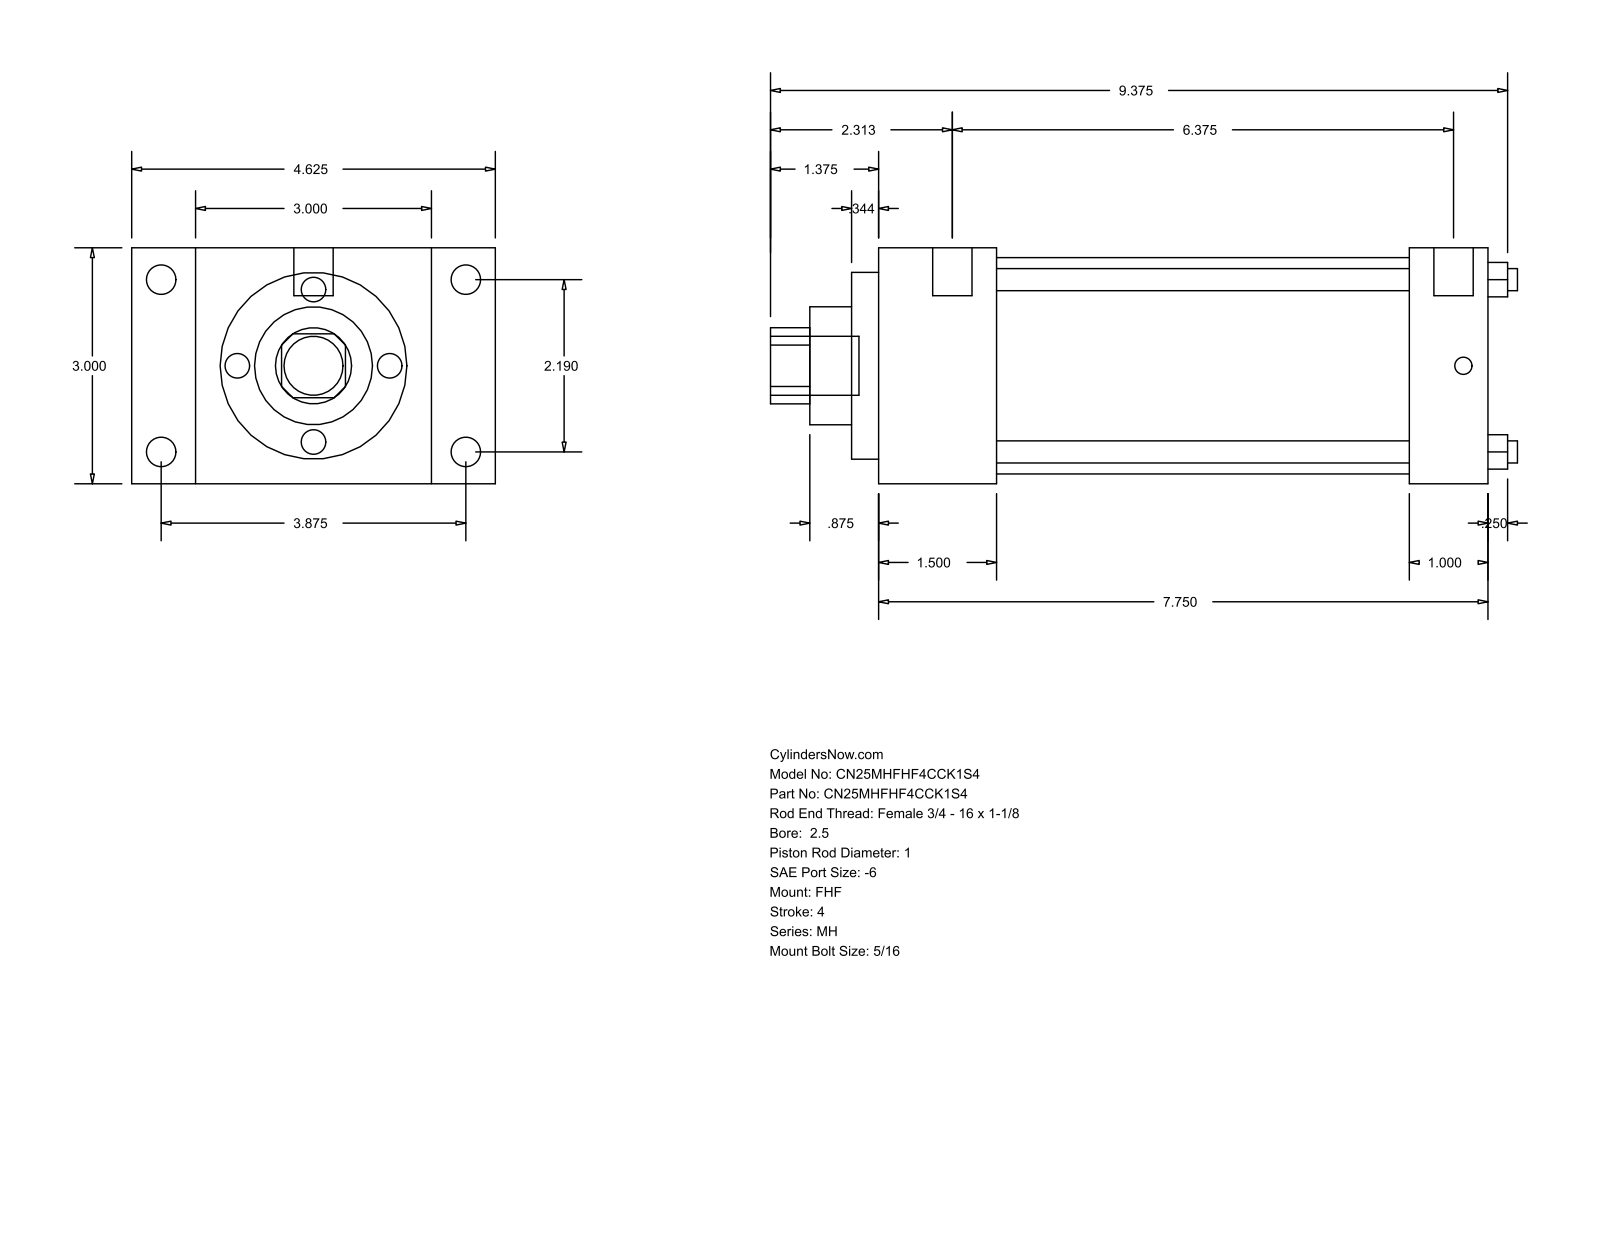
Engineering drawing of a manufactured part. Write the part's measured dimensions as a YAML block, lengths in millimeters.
part_name: "MH_FHF__0250_1"
step_written_by: "GSSL Pune (CONFIG_CONTROL_DESIGN)"
units: millimeters
bodies: {solids: 0, faces: 90, planar: 61, cylindrical: 29, other: 0}
overall_size: [241.3, 117.47, 76.2]
round_holes:
  - {diameter: 7.14, count: 4}
  - {diameter: 25.4, count: 1}
  - {diameter: 38.1, count: 1}
  - {diameter: 60.33, count: 1}
  - {diameter: 69.85, count: 1}
round_bosses_or_shafts:
  - {diameter: 9.53, count: 4}
  - {diameter: 5.56, count: 4}
  - {diameter: 12.7, count: 2}
  - {diameter: 19.05, count: 1}
partial_cylinders:
  - {radius: 12.29, count: 1}
face_to_face_distances: [76.2, 196.86, 38.11, 158.75, 20.64, 96.84, 117.48, 171.46, 133.35, 25.4]
hole_center_spacings: [39.33, 55.62, 78.66]
